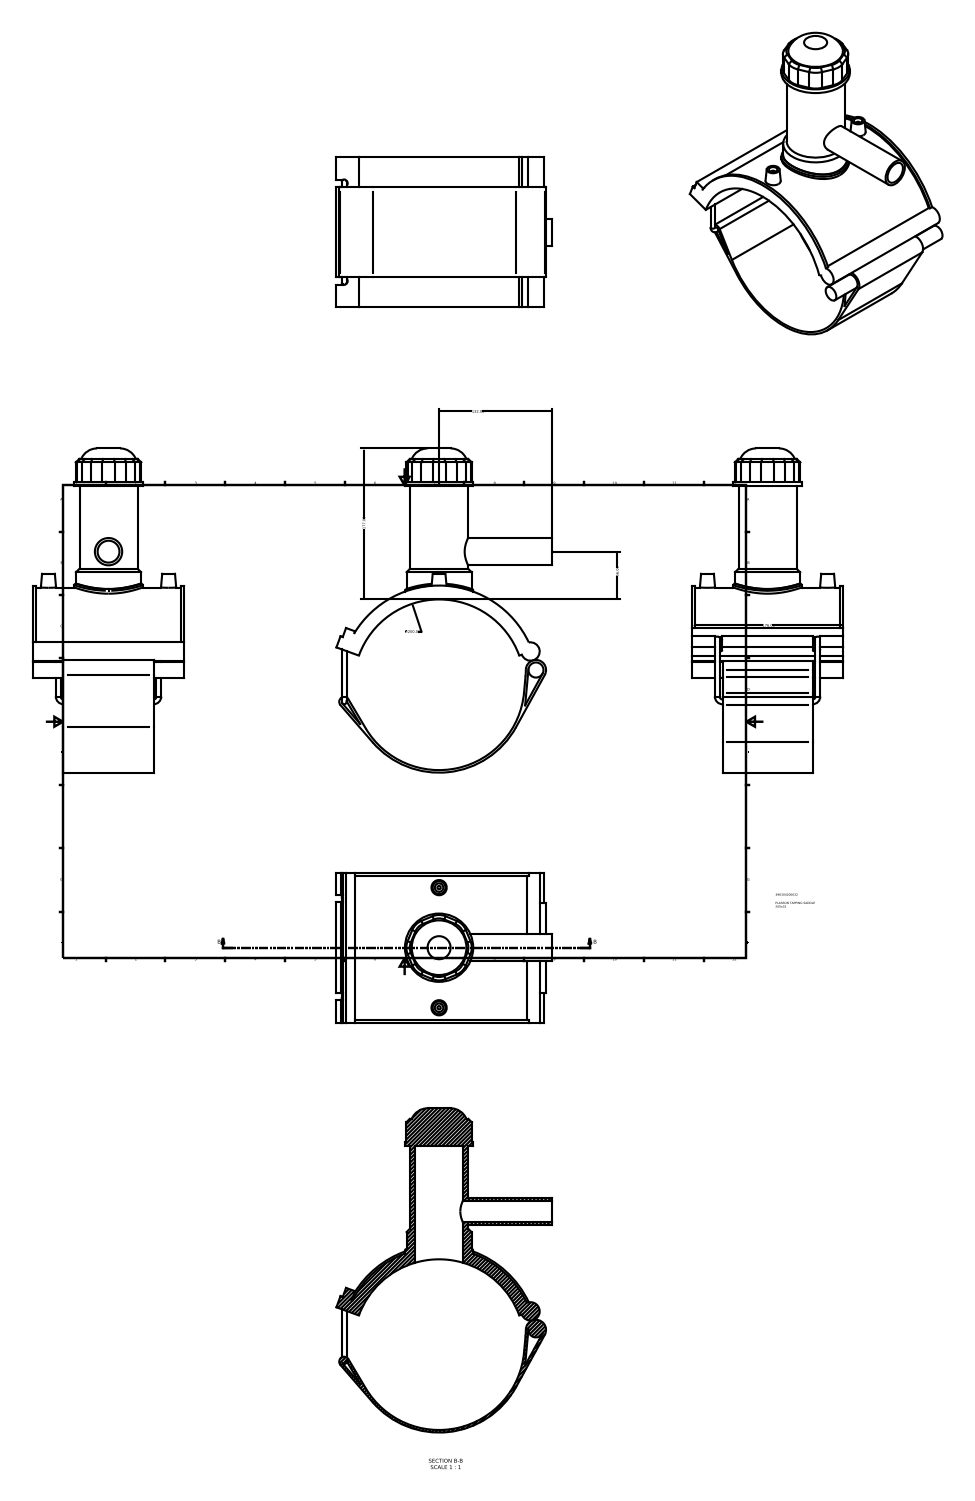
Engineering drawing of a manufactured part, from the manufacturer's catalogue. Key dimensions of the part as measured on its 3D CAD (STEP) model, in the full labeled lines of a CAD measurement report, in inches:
Part name (STEP PRODUCT): 496304200032
STEP written by: Autodesk Inventor 2015 (AUTOMOTIVE_DESIGN)
Units: inches
Bodies: 1 solid, 121 faces (68 planar, 38 cylindrical, 15 other)
Overall size (bounding box): 14.961 × 9.932 × 6.929
Volume: 78.11 in³ · Surface area: 475 in²
Round holes (diameter × count): ⌀0.394 ×2, ⌀1.008 ×1, ⌀2.205 ×1
Round bosses / shafts (diameter × count): ⌀0.22 ×2, ⌀0.157 ×2, ⌀3.15 ×1, ⌀2.992 ×1, ⌀2.677 ×1, ⌀1.26 ×1, ⌀0.696 ×1
Partial cylindrical surfaces — rounded edges, fillets, slot ends (radius × count): R0.787 ×8, R0.165 ×2, R3.937 ×2, R0.11 ×1, R0.228 ×1, R0.424 ×1, R0.467 ×1, R4.055 ×1
Main face-to-face distances: 0.118, 6.929, 0.119, 1.386, 5.543, 0.441, 0.551, 0.106, 0.993, 0.11
Hole centre spacings: 2.772, 5.543
